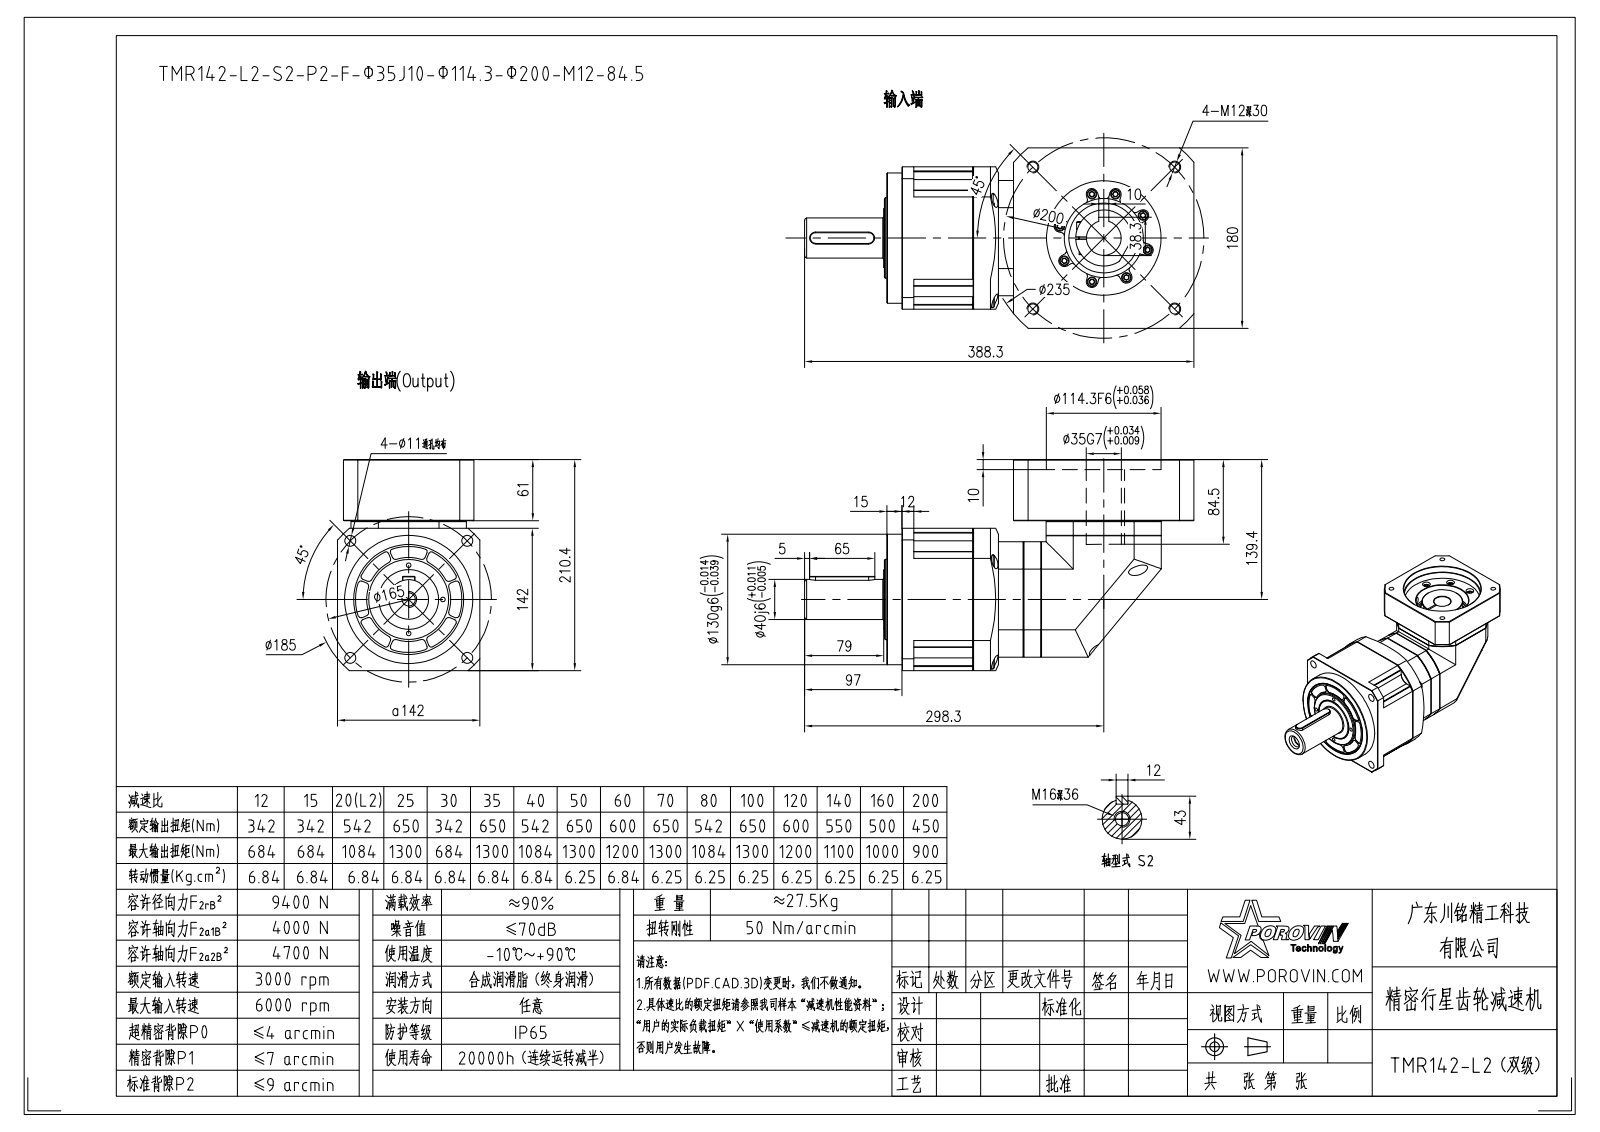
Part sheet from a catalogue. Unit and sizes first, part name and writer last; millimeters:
Units: millimetres
Overall size (bounding box): 389.52 × 210.4 × 182.45
Round holes (diameter × count): ⌀6.5 ×18, ⌀6.68 ×17, ⌀5 ×13, ⌀6.8 ×7, ⌀11 ×6, ⌀14 ×5, ⌀9 ×4, ⌀10.2 ×4, ⌀10.5 ×4, ⌀11.9 ×4, ⌀8.5 ×1, ⌀13.6 ×1
Round bosses / shafts (diameter × count): ⌀10 ×17, ⌀9.88 ×17, ⌀6 ×17, ⌀13 ×5, ⌀8 ×5, ⌀130 ×1, ⌀99 ×1, ⌀80 ×1
Partial cylindrical surfaces — rounded edges, fillets, slot ends (radius × count): R2 ×48, R1 ×40, R5.75 ×8, R10.5 ×4, R6 ×2, R65 ×2, R5 ×1, R6.75 ×1
Main face-to-face distances: 13.5, 128.5, 50.3, 61, 18, 180.02, 68.3, 68.1, 17.8, 142
Hole centre spacings: 45.25, 83.61, 34.63, 63.99, 90.5, 0.74, 12.31, 21.17
Volume: 5 225 000 mm³ · Surface area: 498 535 mm²
Bodies: 49 solids, 1573 faces (663 planar, 613 cylindrical, 297 other)
Part name (STEP PRODUCT): SPRING_LOCK_WASHERS--NORMAL_TYP; HEXAGON_SOCKET_HEAD_CAP_S-18760; HEXAGON_SOCKET_HEAD_CAP_S-18817; TMR1150003 (+8 more)
STEP written by: CREO PARAMETRIC BY PTC INC, 2020053 (CONFIG_CONTROL_DESIGN)
